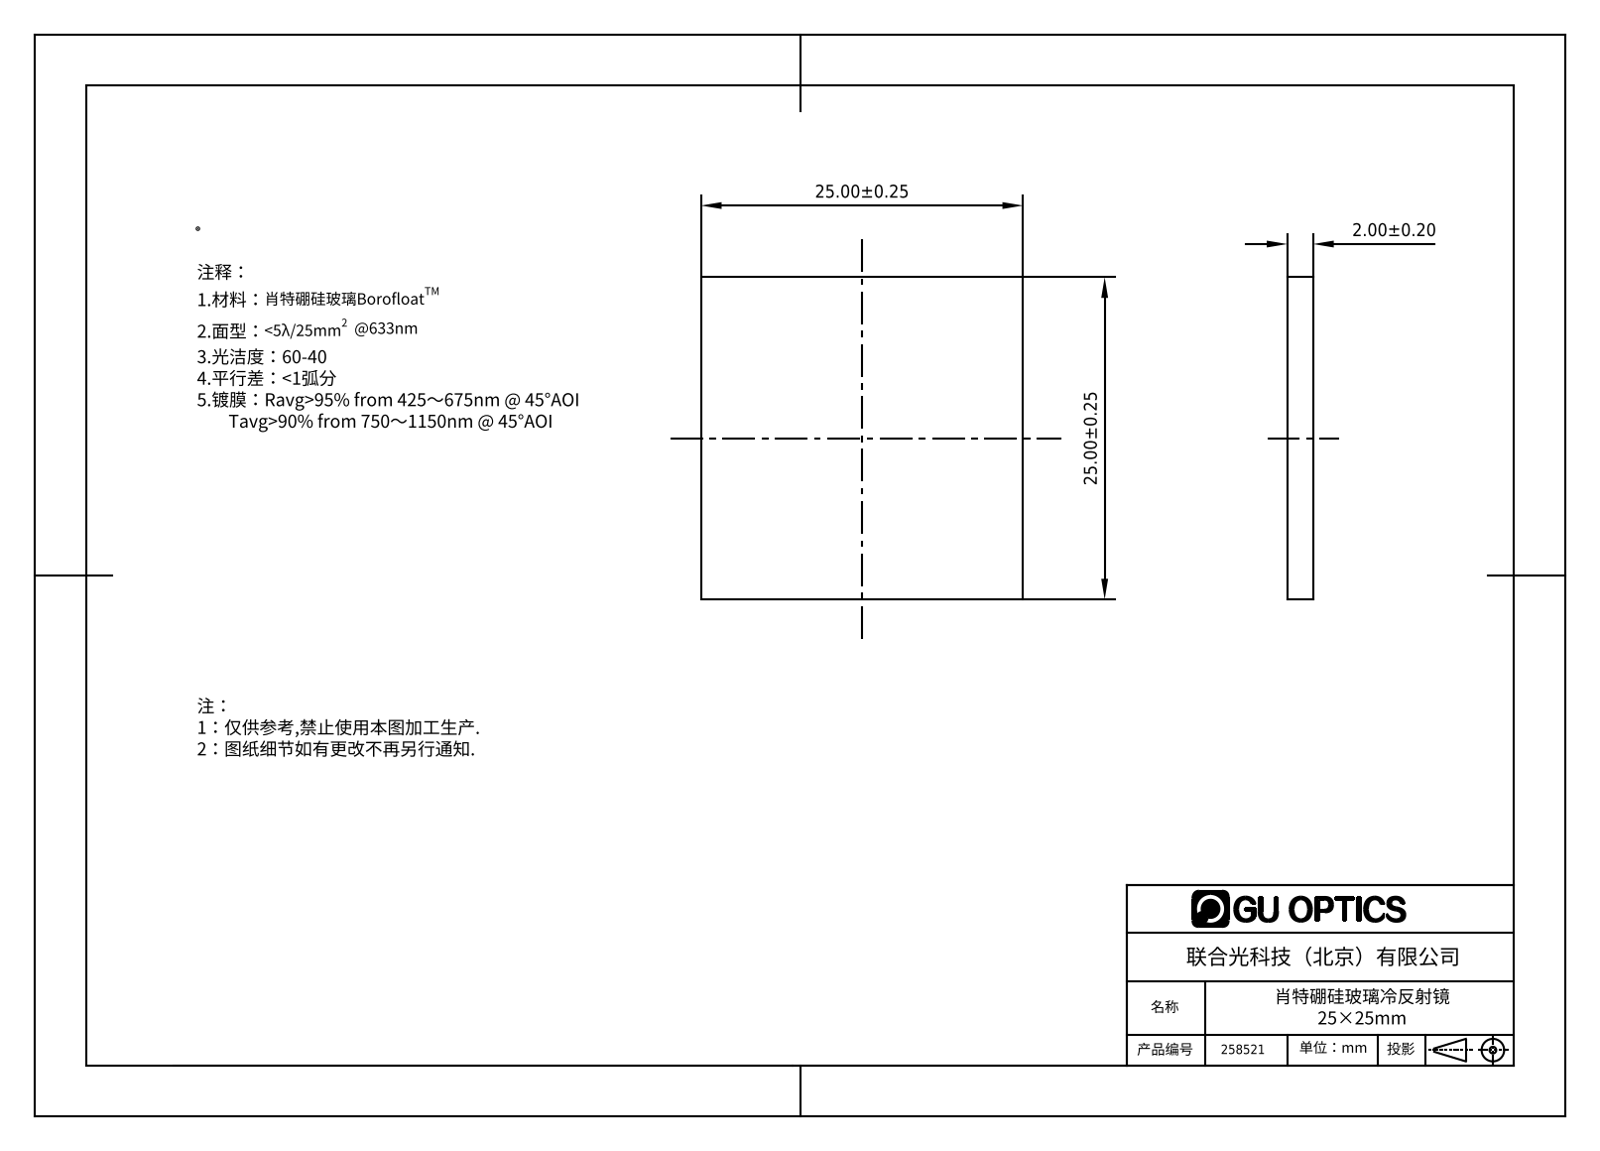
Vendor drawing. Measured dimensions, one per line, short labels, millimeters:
name: 258512
written by: SolidWorks 2016 (AUTOMOTIVE_DESIGN)
unit: mm
bodies: 1 solid, 6 faces (6 planar, 0 cylindrical, 0 other)
size: 25 × 25 × 2
volume: 1 250 mm³; area: 1 450 mm²
face distances: 2, 25
